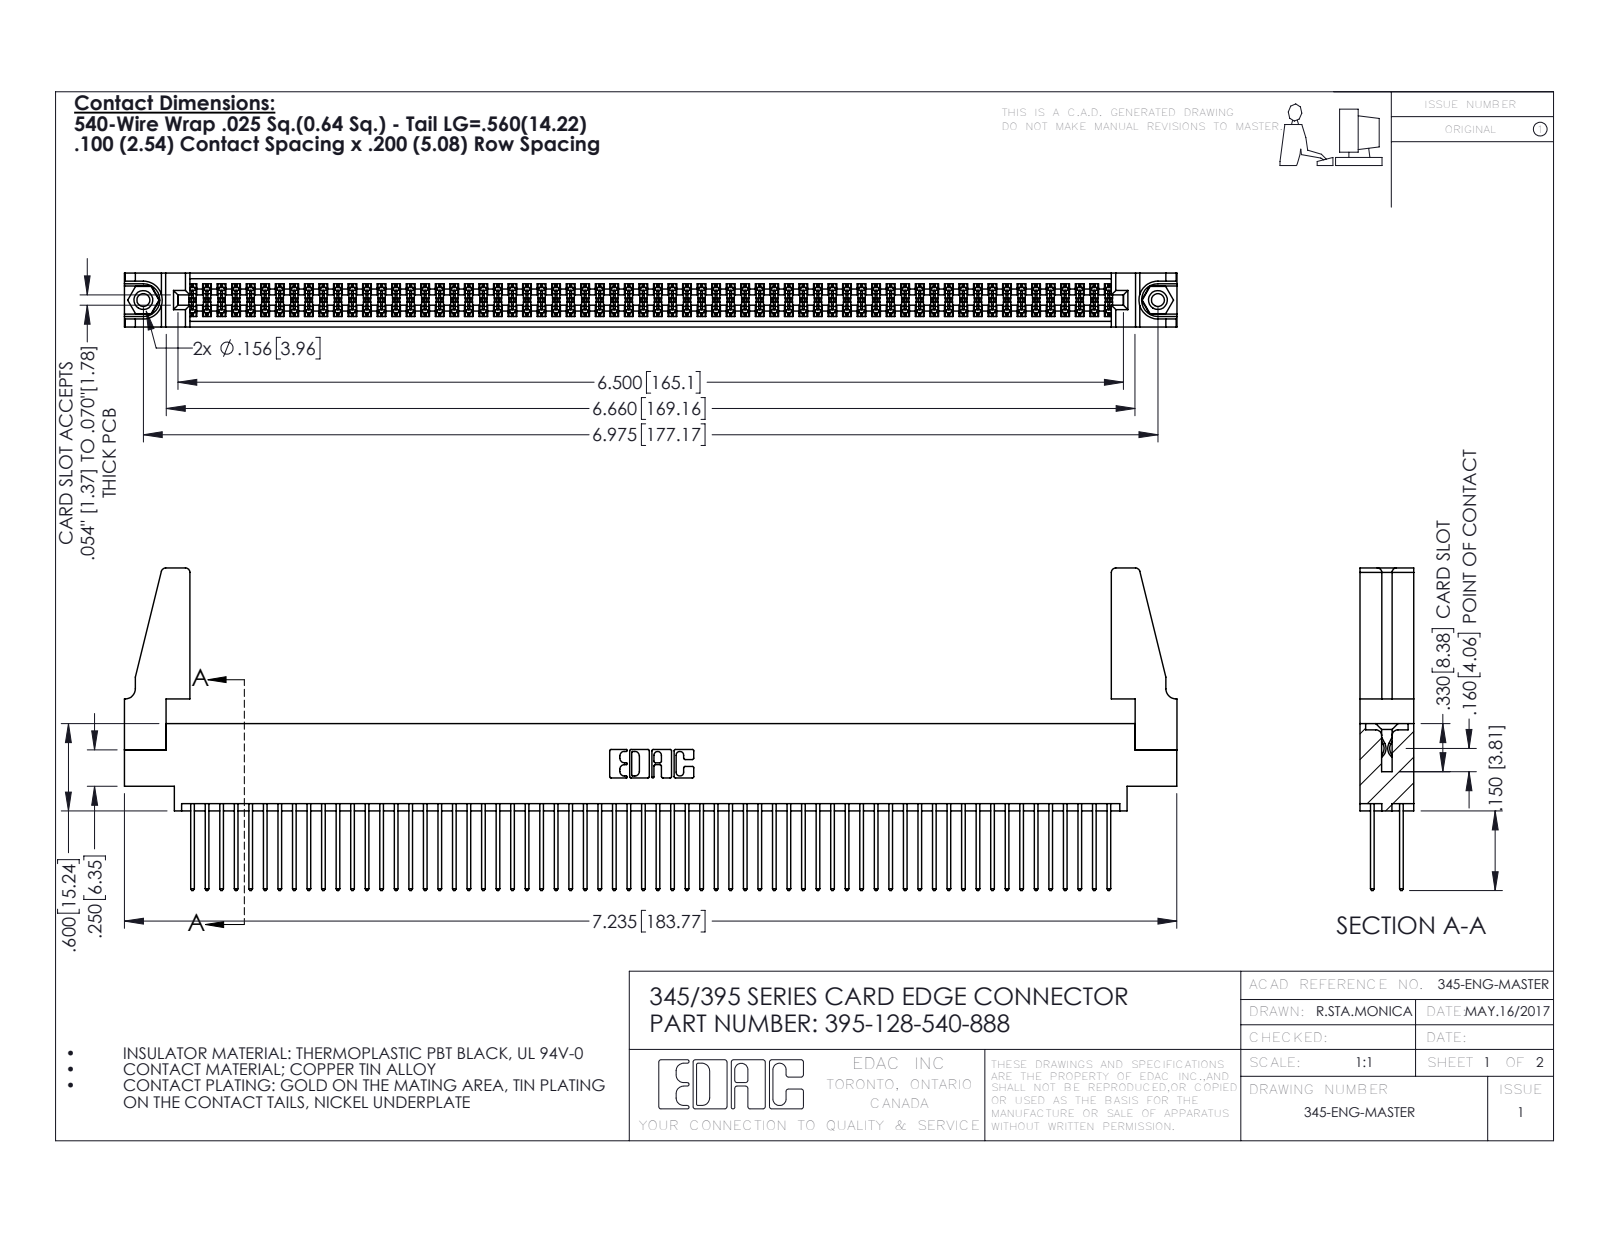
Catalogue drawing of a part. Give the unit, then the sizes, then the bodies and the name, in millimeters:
Units: millimetres
Overall size (bounding box): 183.8 × 56.3 × 9.4
Round holes (diameter × count): ⌀2.3 ×2, ⌀3.2 ×2, ⌀4 ×2, ⌀1.6 ×1
Round bosses / shafts (diameter × count): ⌀3.9 ×2
Partial cylindrical surfaces — rounded edges, fillets, slot ends (radius × count): R0.2 ×192, R0.3 ×128, R0.3 ×22, R0.8 ×8, R0.2 ×6, R0.8 ×6, R0.7 ×3, R0.4 ×2
Main face-to-face distances: 1.8, 7.6, 2.5, 6.9, 0.6, 5.1, 9.4, 5.7, 4.4, 3.8
Hole centre spacings: 6.9, 171.2, 177.2
Volume: 21 680 mm³ · Surface area: 33 190 mm²
Bodies: 133 solids, 6654 faces (4380 planar, 2258 cylindrical, 16 other)
Part name (STEP PRODUCT): 345 Part_0.170 Offset - 0.156 Dia-TH; 345-292-001_345-293-140; 345-250-001_345-250-001-102; 395-128-540-888 (+1 more)
STEP written by: SolidWorks 2016 (CONFIG_CONTROL_DESIGN)
